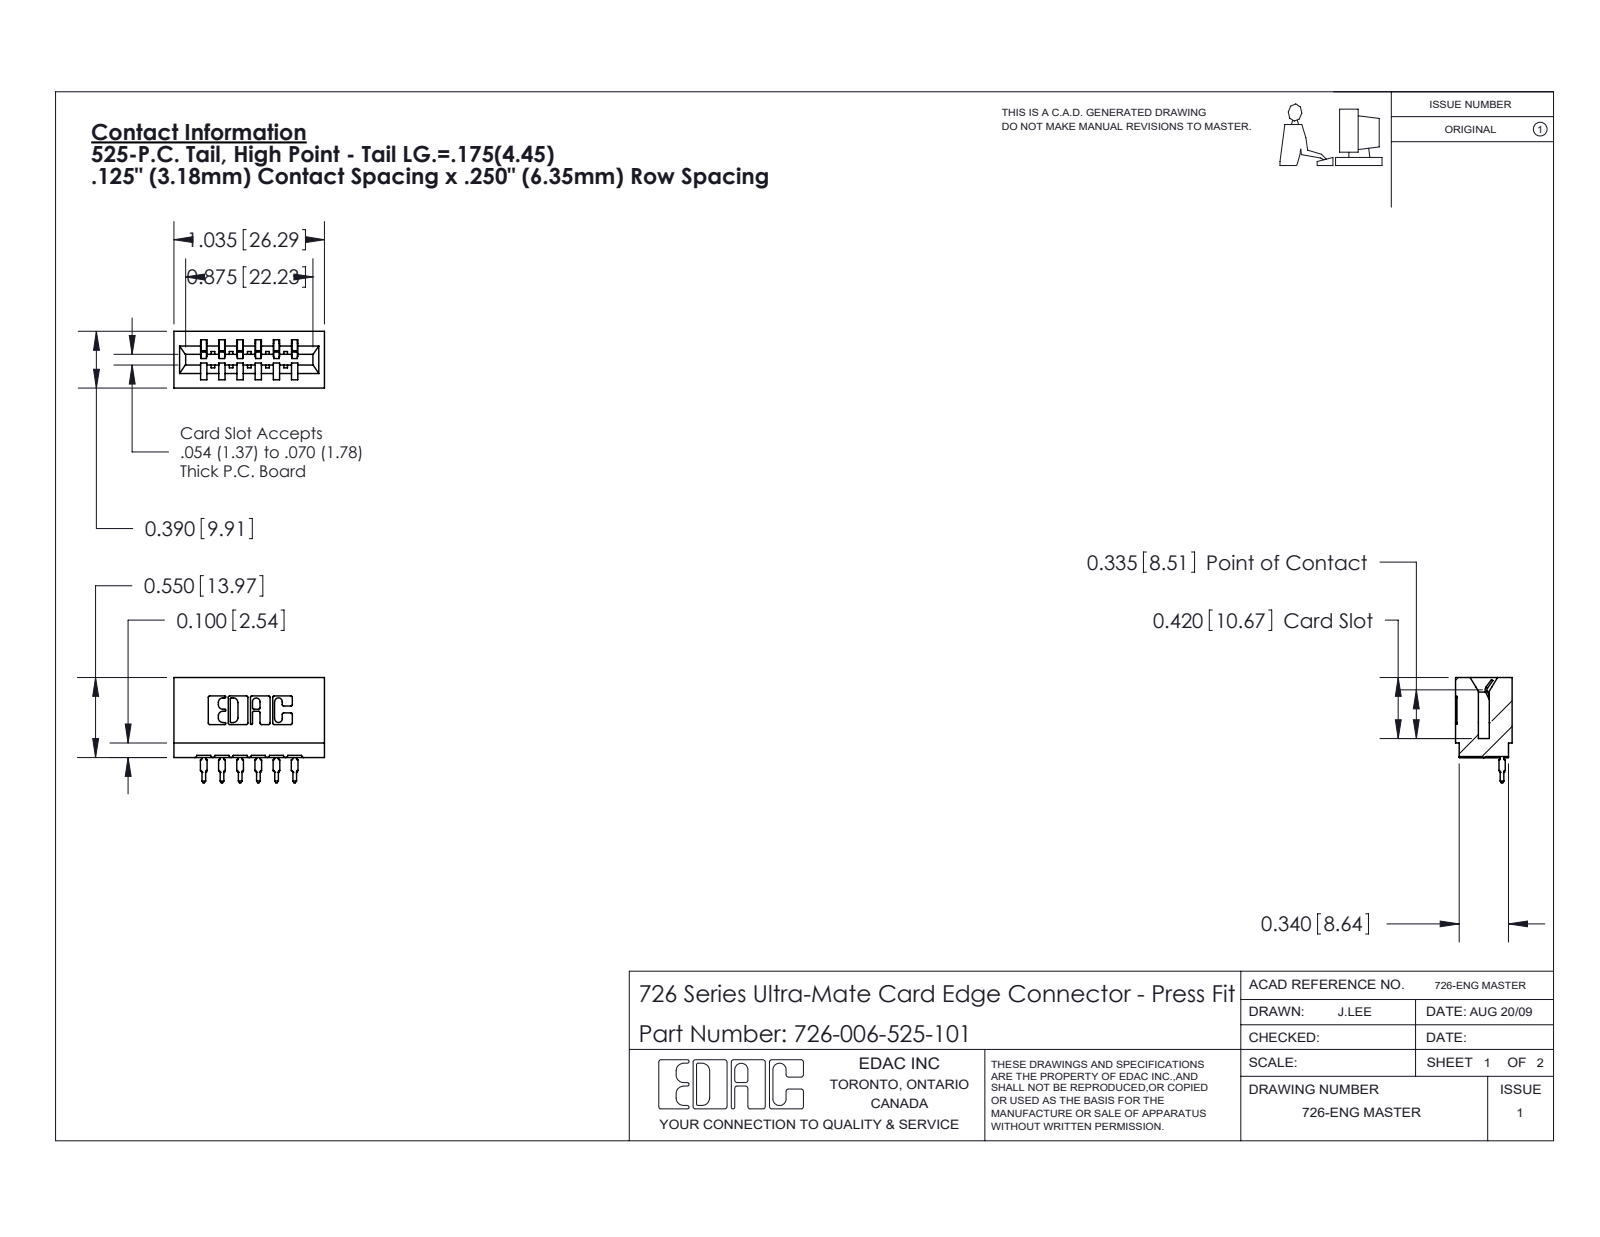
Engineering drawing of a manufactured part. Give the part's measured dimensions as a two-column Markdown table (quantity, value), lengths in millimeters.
| quantity | value |
| --- | --- |
| part name | 726 Part_.515 Slot Depth - 01; 746-292-001_525; 726-006-525-101 |
| STEP written by | SolidWorks 2020 (CONFIG_CONTROL_DESIGN) |
| units | millimeters |
| bodies | 7 solids, 745 faces (433 planar, 156 cylindrical, 156 other) |
| overall size | 26.3 × 18.4 × 9.9 |
| volume | 2 540 mm³ |
| surface area | 3 327 mm² |
| partial cylindrical surfaces (radius × count) | 0.3 × 22, 0.5 × 12, 0.4 × 7, 0.2 × 6, 0.8 × 6, 0.1 × 4, 0.3 × 4, 0.7 × 3 |
| main face-to-face distances | 6.4, 3.2, 1.1, 8.5, 1.4, 3.2, 7.4, 9.5, 12.7, 5.3 |
